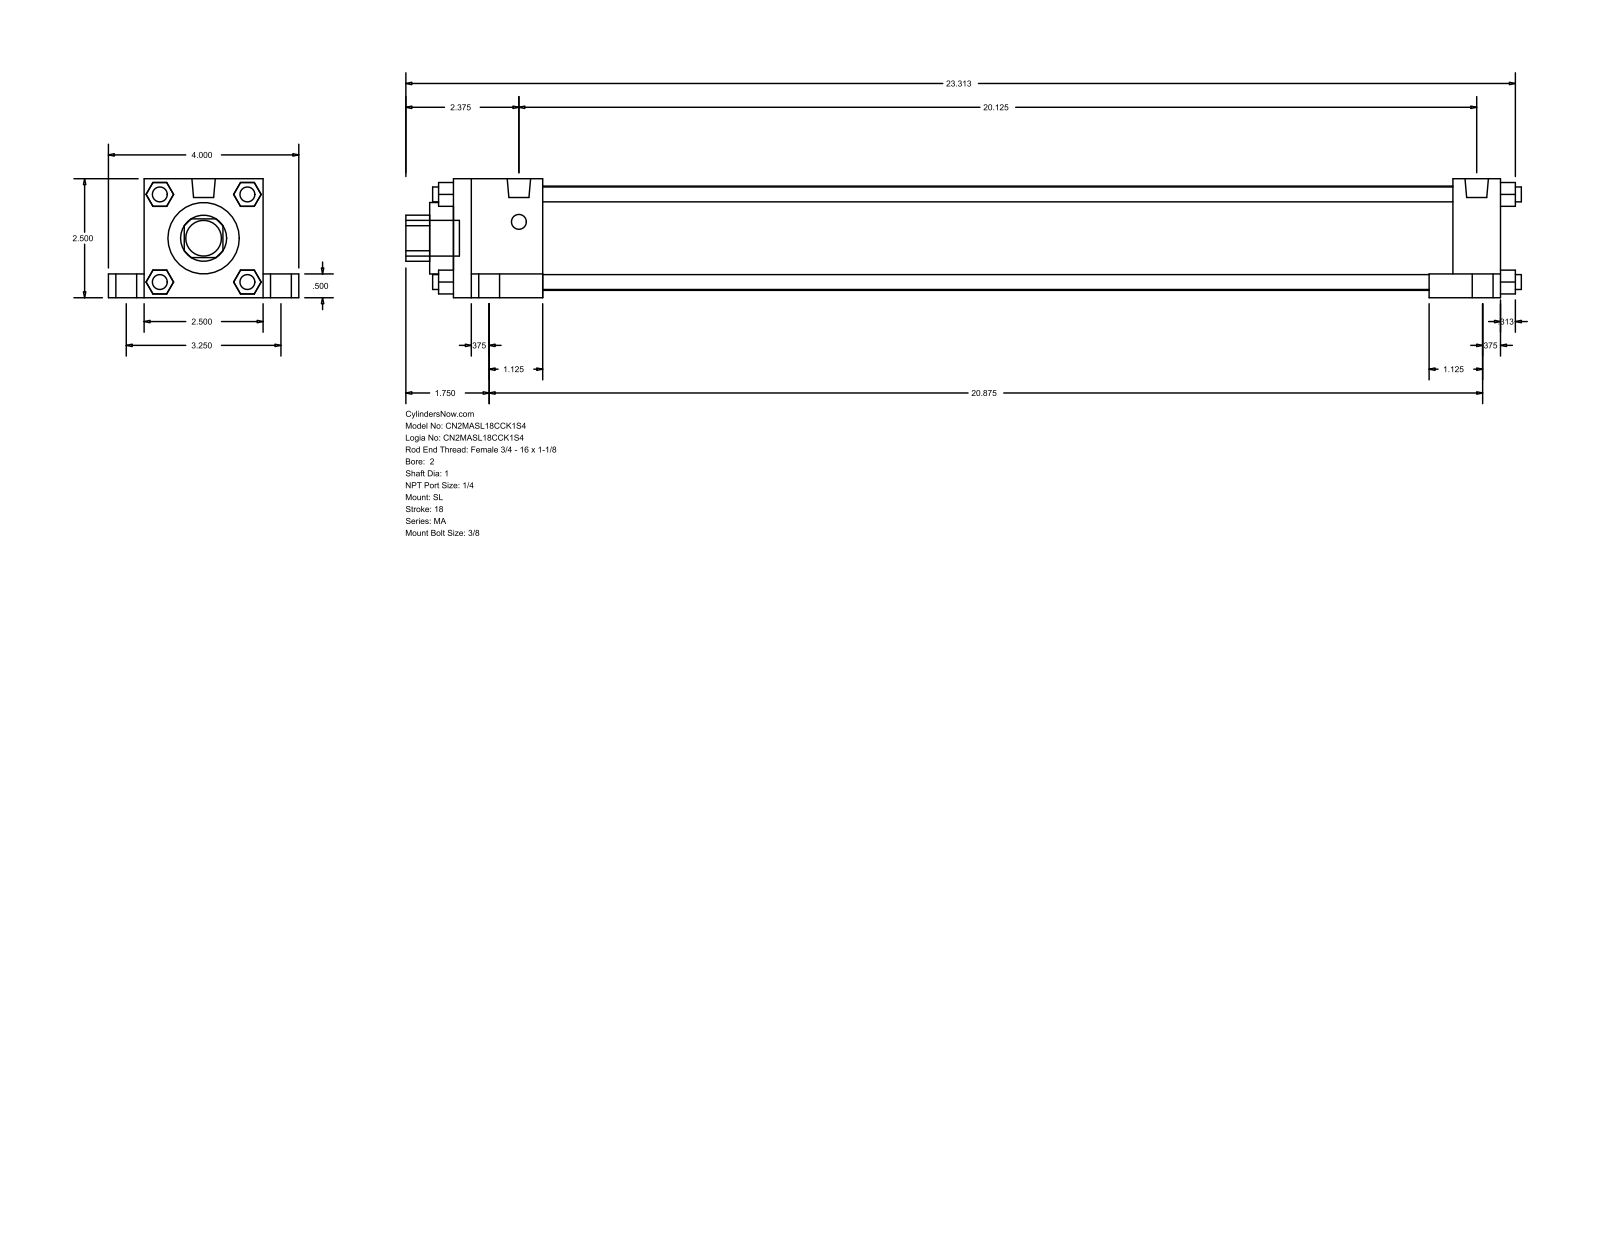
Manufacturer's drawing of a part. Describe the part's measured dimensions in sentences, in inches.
The part is named "MA_SL__0200_1". Its 3-D file was written by "GSSL Pune (CONFIG_CONTROL_DESIGN)". It is 0 solids with 148 faces: 112 planar, 36 cylindrical and 0 other. Overall it measures 23.437 by 4 by 2.5 inches. Round holes: 1 of diameter 1, 1 of diameter 1.5, 1 of diameter 2.19. Round bosses or shafts: 8 of diameter 0.313, 4 of diameter 0.687, 4 of diameter 0.437, 2 of diameter 0.492, 1 of diameter 0.75. Partial cylindrical surfaces (rounded edges, fillets, slot ends): 1 of radius 0.484. The main face-to-face distances are 2.5, 0.5, 22, 0.75, 3.25, 1, 2, 1.875, 20.125, 21.
